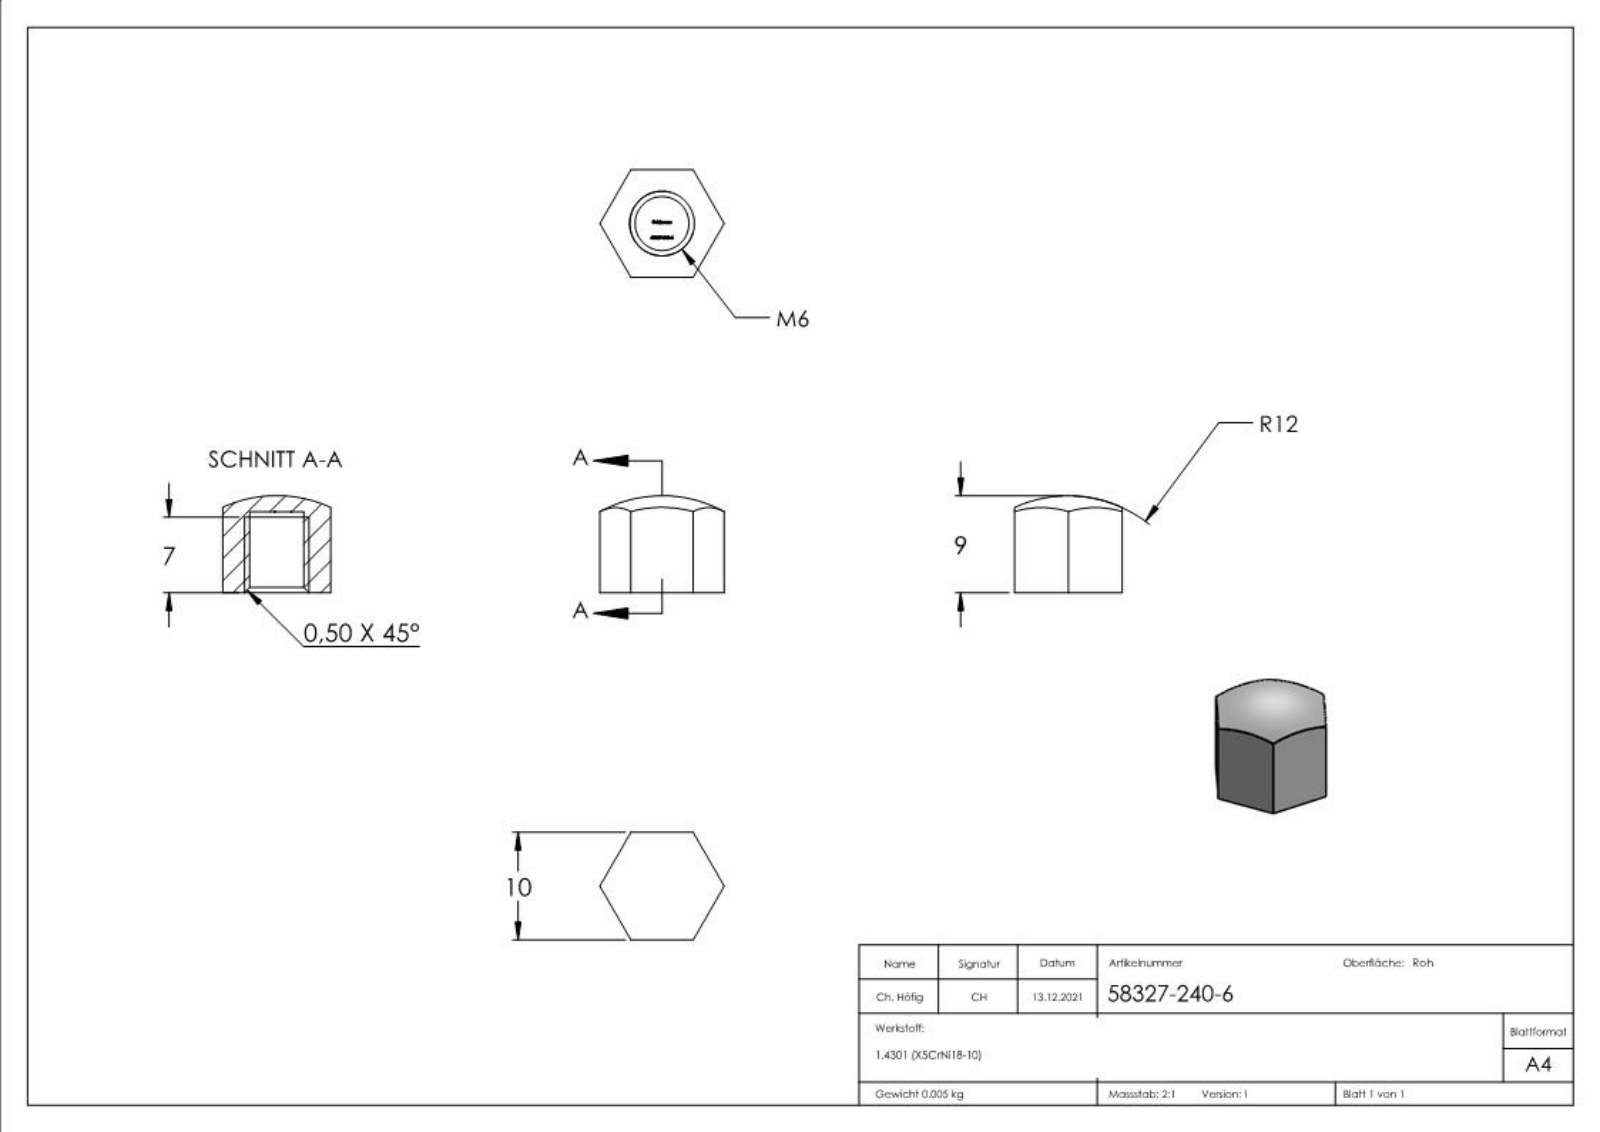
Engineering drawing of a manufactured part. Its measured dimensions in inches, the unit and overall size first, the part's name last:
Units: inches
Overall size (bounding box): 0.455 × 0.394 × 0.354
Round holes (diameter × count): ⌀0.197 ×1
Main face-to-face distances: 0.394, 0.295, 0.299, 0.057, 0.034, 0.035, 0.197, 0.013, 0.051, 0.059
Volume: 0.035 in³ · Surface area: 0.873 in²
Bodies: 1 solid, 260 faces (140 planar, 1 cylindrical, 119 other)
Part name (STEP PRODUCT): 58327-240-6
STEP written by: SolidWorks 2018 (CONFIG_CONTROL_DESIGN)
